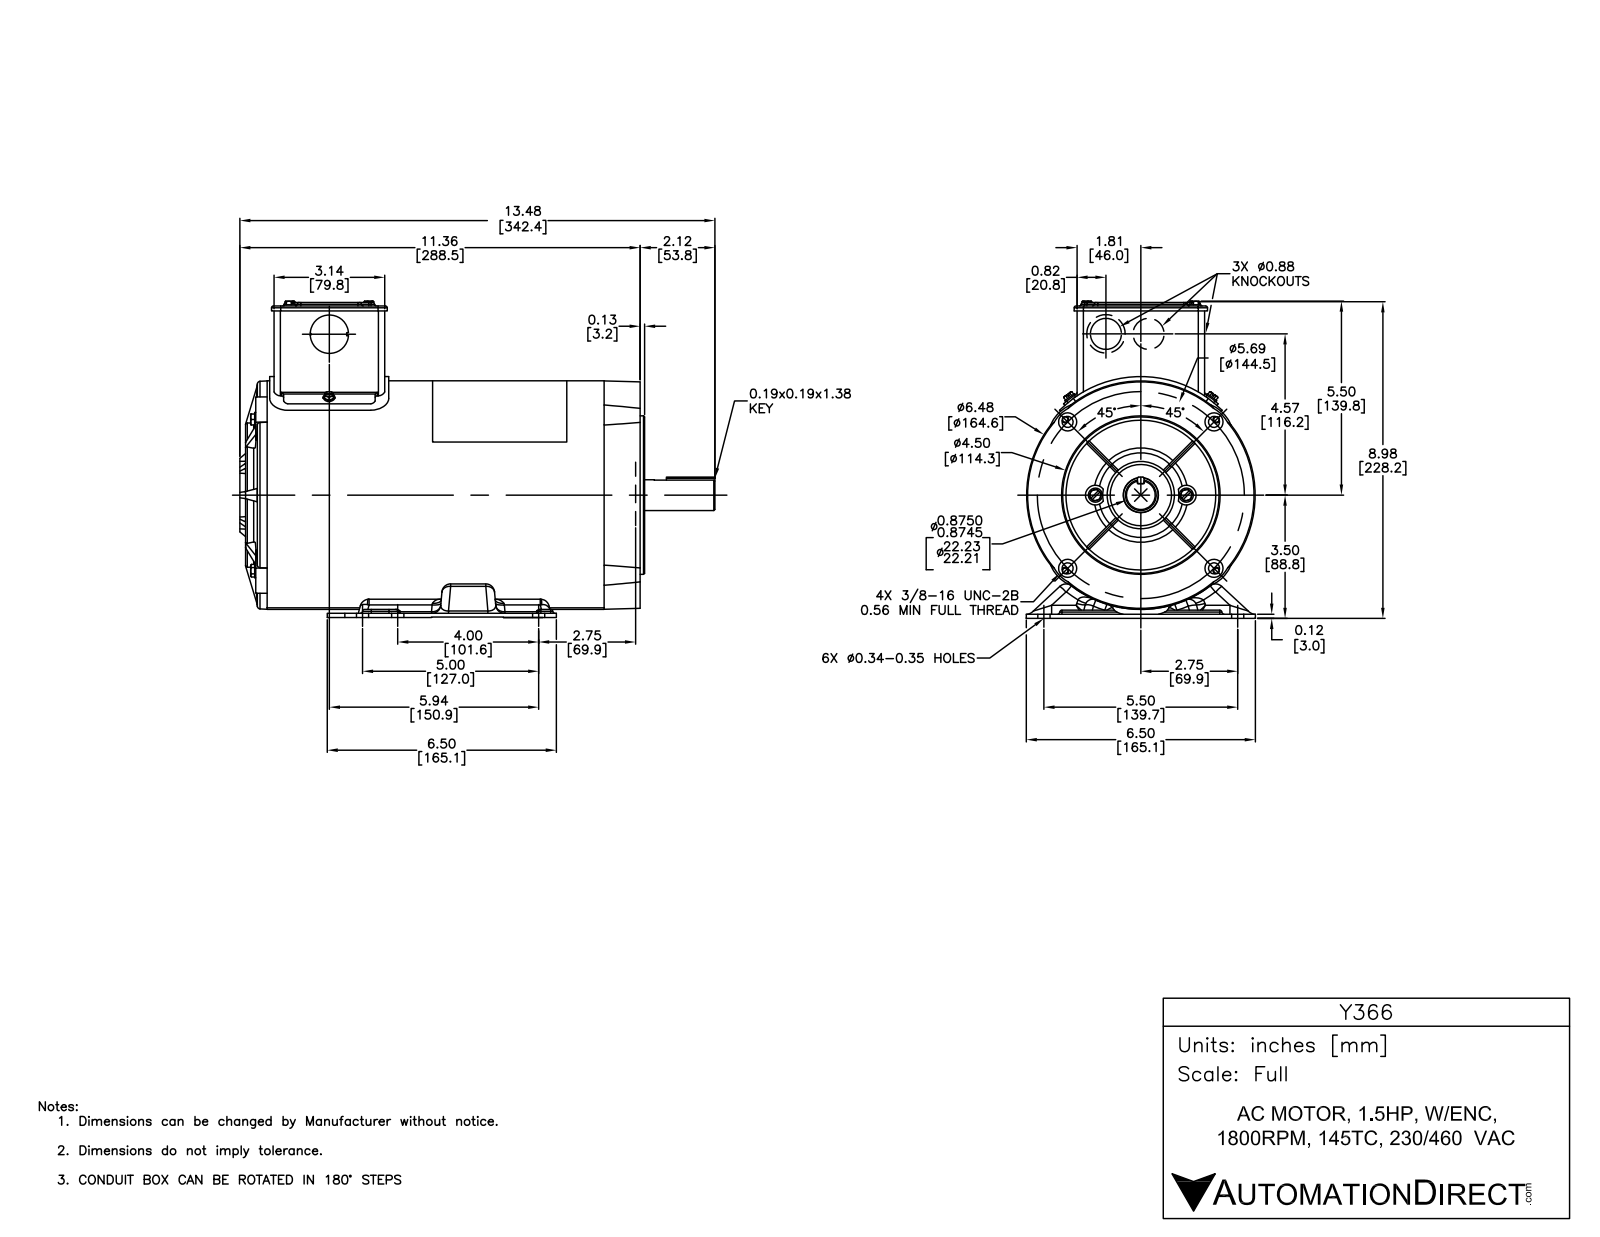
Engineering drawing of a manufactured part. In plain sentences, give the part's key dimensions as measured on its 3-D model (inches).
The part is named "104963-956_Rev04 R1". Its 3-D file was written by "SolidWorks 2017 (AUTOMOTIVE_DESIGN)". It is 27 solids with 3386 faces: 1092 planar, 705 cylindrical and 1589 other. Overall it measures 13.489 by 8.895 by 6.5 inches. Its volume is 56.91 cubic inches and its surface area 926.2 square inches. Round holes: 6 of diameter 0.178, 6 of diameter 0.28, 6 of diameter 0.345, 5 of diameter 0.12, 4 of diameter 0.125, 4 of diameter 0.159, 4 of diameter 0.215, 4 of diameter 0.218, 4 of diameter 0.225, 4 of diameter 0.25, 4 of diameter 0.313, 3 of diameter 0.88. Round bosses or shafts: 6 of diameter 0.399, 6 of diameter 0.365, 6 of diameter 0.25, 6 of diameter 0.19, 4 of diameter 0.166, 4 of diameter 0.164, 2 of diameter 0.335, 2 of diameter 0.335. Partial cylindrical surfaces (rounded edges, fillets, slot ends): 64 of radius 0.05, 37 of radius 0.06, 34 of radius 0.25, 29 of radius 0.03, 12 of radius 0.175, 12 of radius 0.2, 10 of radius 0.02, 10 of radius 0.12. The main face-to-face distances are 0.06, 0.119, 3.56, 0.1, 0.041, 8.726, 8.607, 8.666, 8.547, 3.08. The hole center spacings are 1.82, 2.4, 4.22, 4.222, 4.224, 4.287, 0.09, 0.094.
